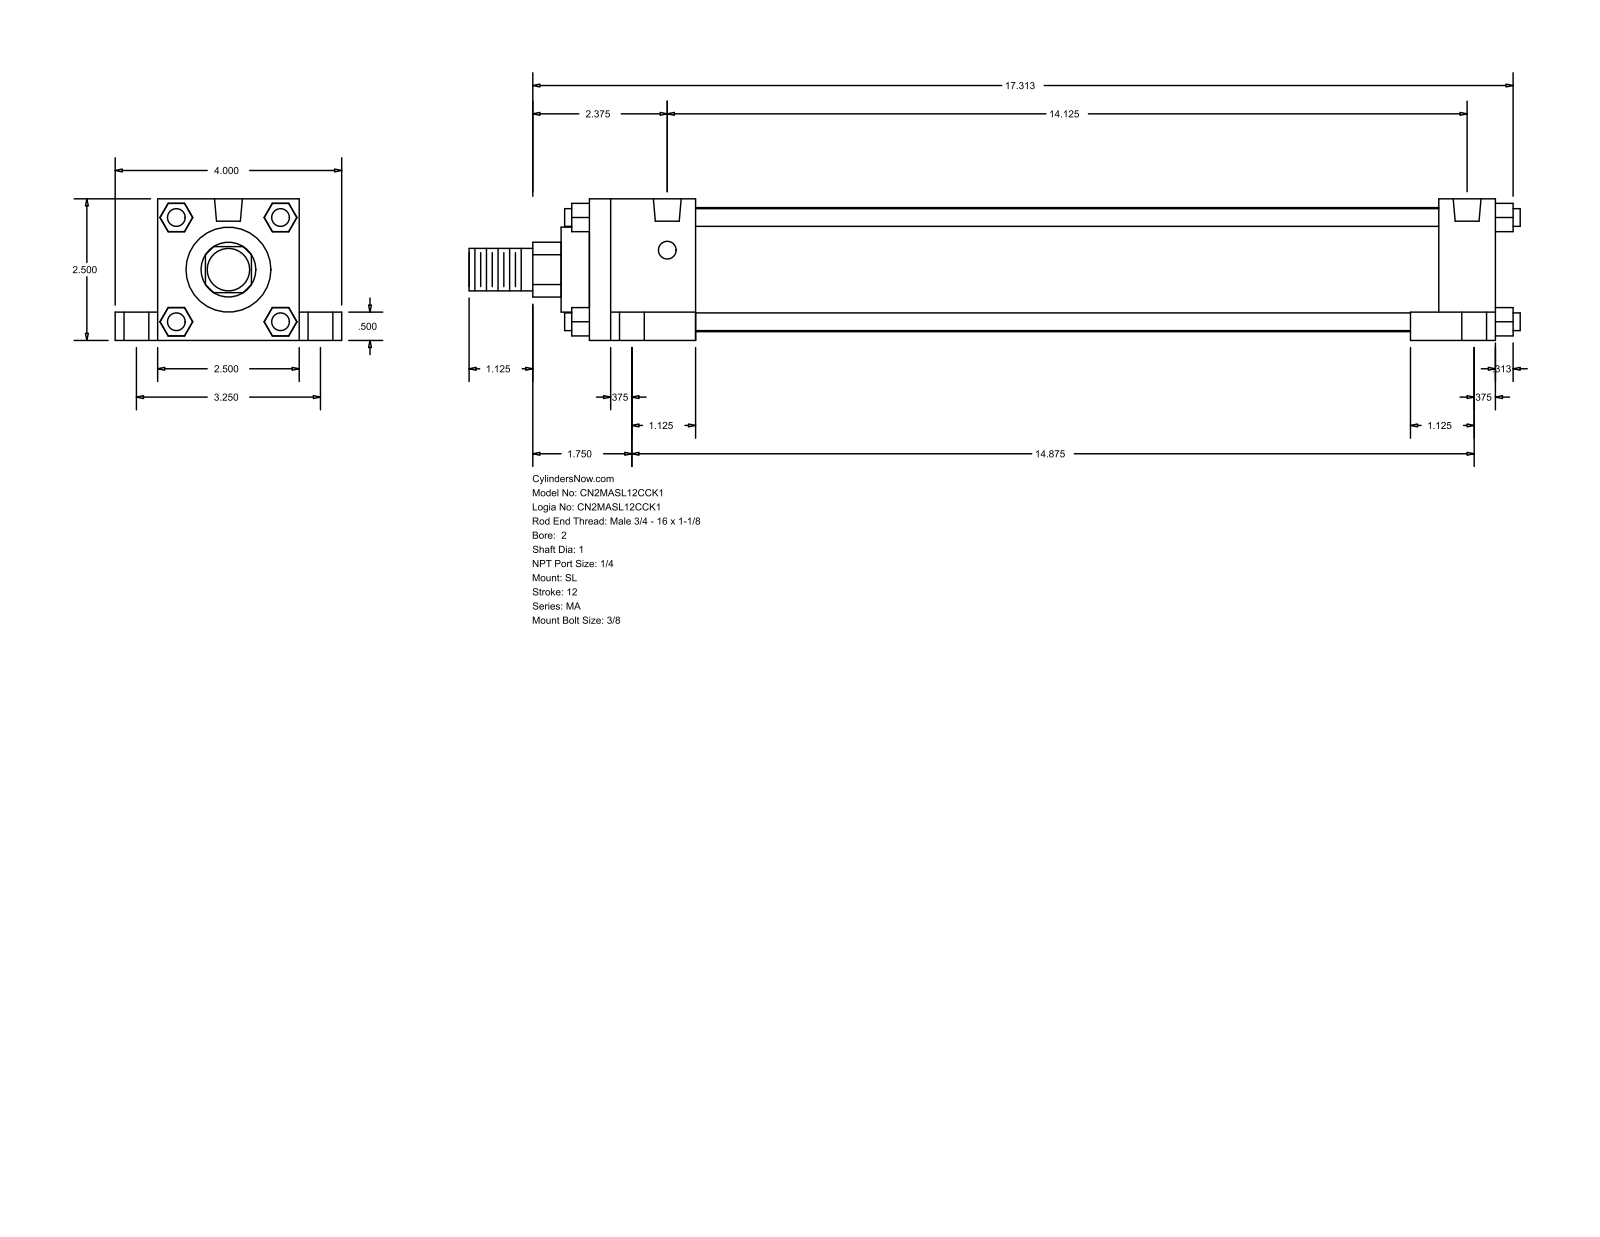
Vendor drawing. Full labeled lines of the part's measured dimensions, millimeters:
Part name (STEP PRODUCT): MA_SL__0200_1
STEP written by: GSSL Pune (CONFIG_CONTROL_DESIGN)
Units: millimetres
Bodies: 0 solids, 148 faces (112 planar, 36 cylindrical, 0 other)
Overall size (bounding box): 471.49 × 101.6 × 63.5
Round holes (diameter × count): ⌀7.94 ×4, ⌀11.11 ×4, ⌀17.46 ×4, ⌀12.49 ×2
Round bosses / shafts (diameter × count): ⌀7.94 ×4, ⌀55.63 ×1, ⌀38.1 ×1, ⌀25.4 ×1, ⌀19.05 ×1
Partial cylindrical surfaces — rounded edges, fillets, slot ends (radius × count): R12.29 ×1
Main face-to-face distances: 63.5, 12.7, 406.4, 19.05, 82.55, 25.4, 50.8, 47.63, 358.77, 381
Hole centre spacings: 41.39, 44.22, 82.54, 358.77, 364.29, 376.92, 377.82, 386.73
